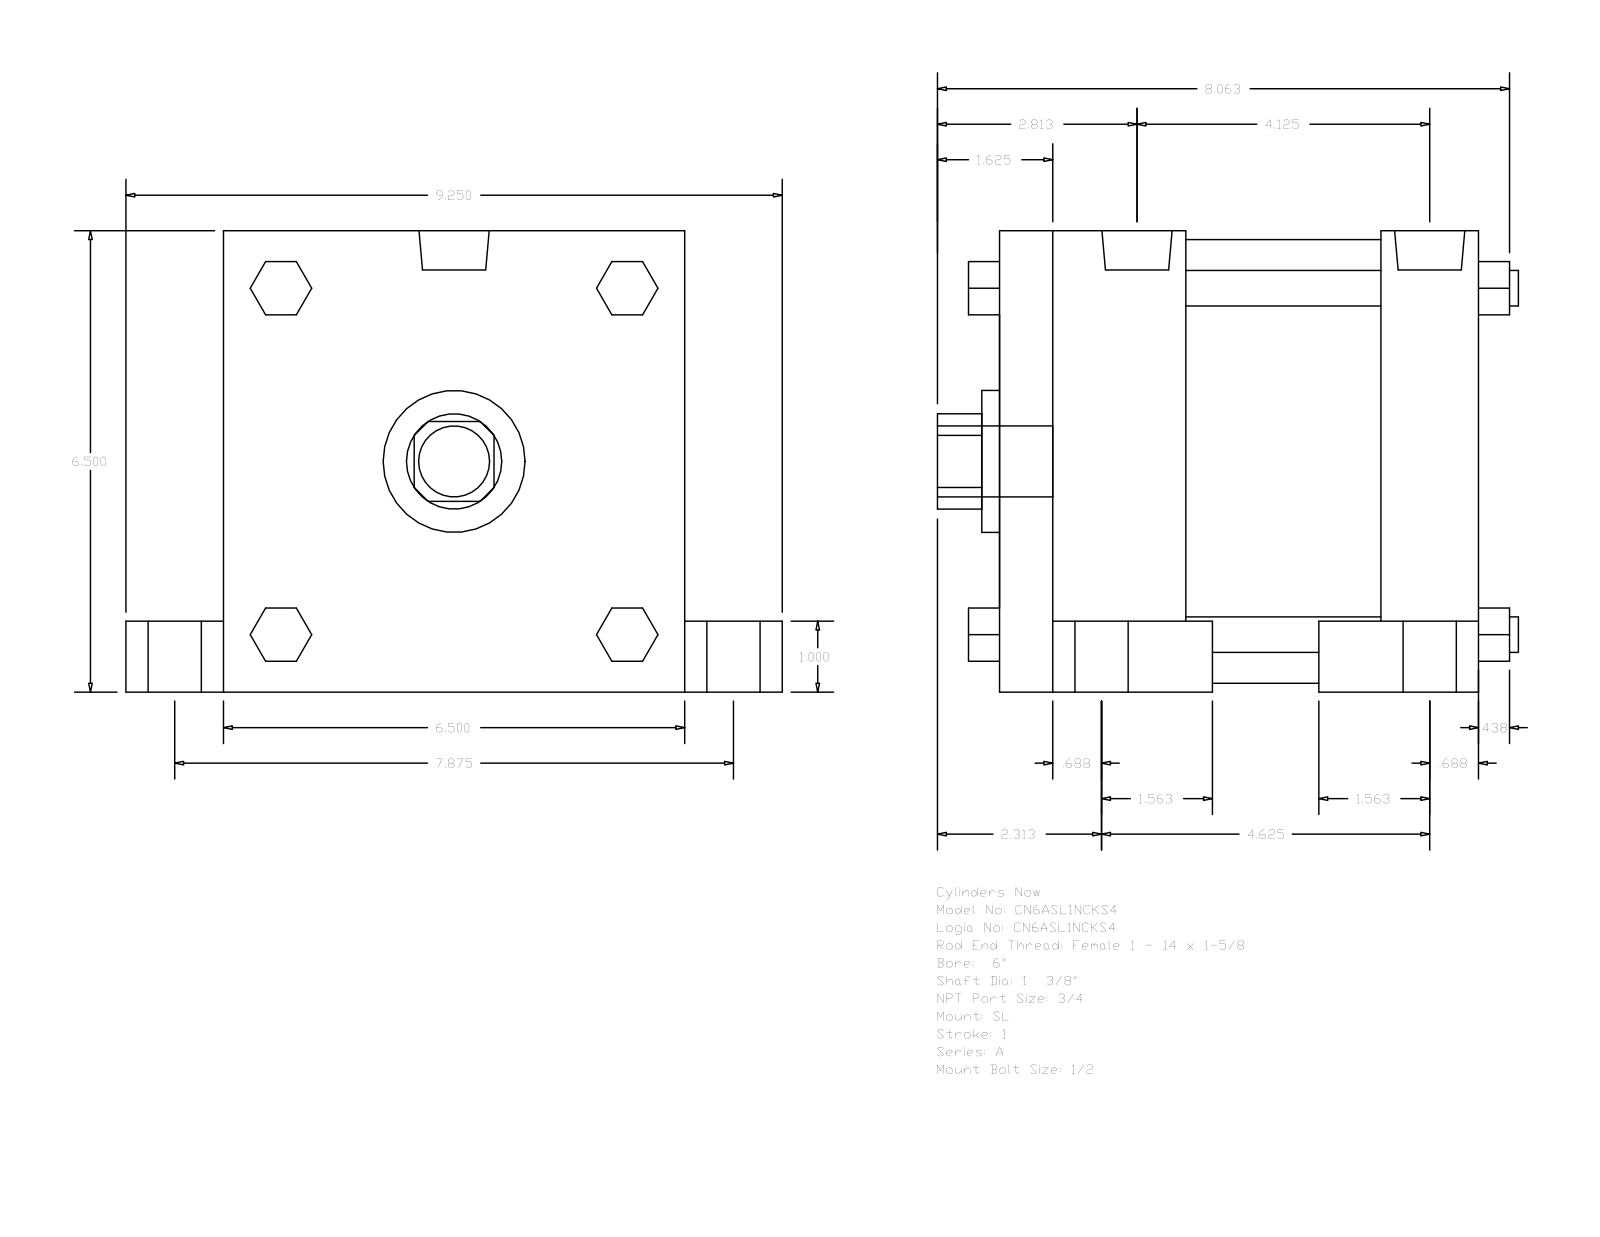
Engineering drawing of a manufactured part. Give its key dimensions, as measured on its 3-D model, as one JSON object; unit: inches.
{"part_name": "A_SL__0600_1.375", "step_written_by": "GSSL Pune (CONFIG_CONTROL_DESIGN)", "units": "inches", "bodies": {"solids": 0, "faces": 150, "planar": 114, "cylindrical": 36, "other": 0}, "overall_size": [9.25, 8.187, 6.5], "round_holes": [[1.375, 1], [2, 1], [6.25, 1]], "round_bosses_or_shafts": [[1, 5], [0.75, 4], [0.594, 4], [0.5, 4], [0.989, 2]], "partial_cylinders_radius": [[0.672, 1]], "face_to_face_distances": [6.5, 6.75, 2.625, 4.125, 5.375, 2.75, 1.375, 1, 5.5, 1.375]}
